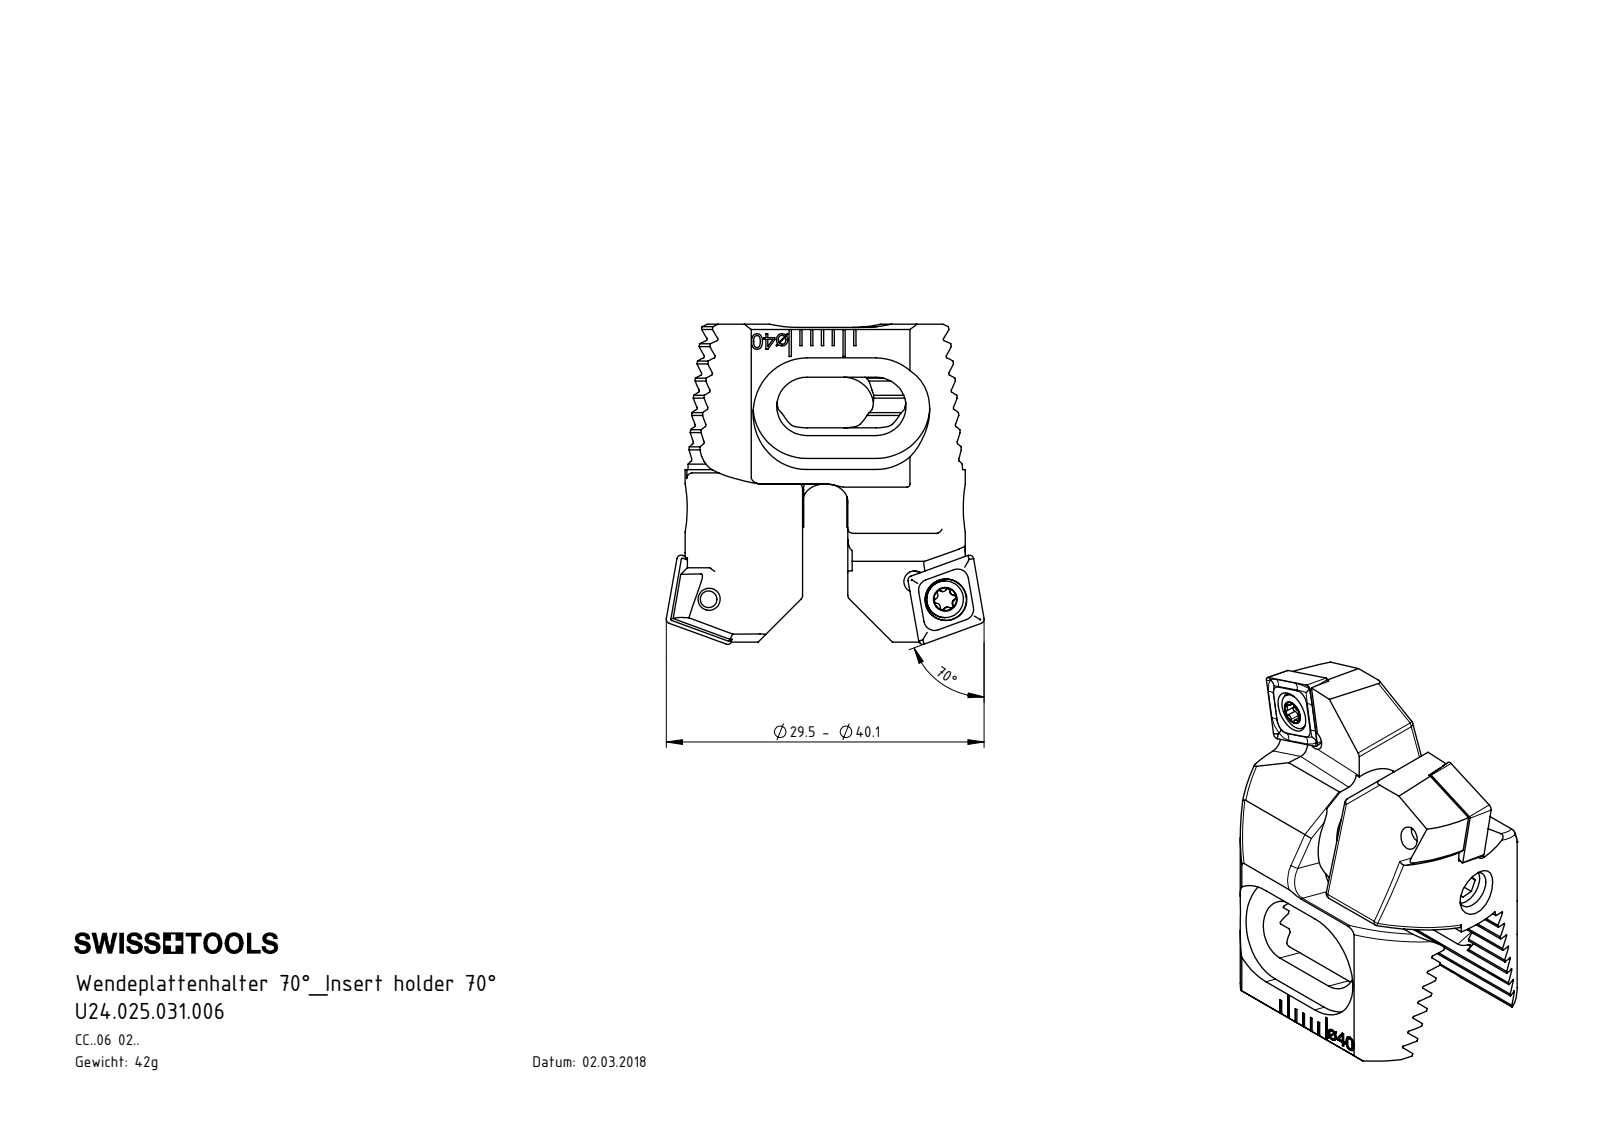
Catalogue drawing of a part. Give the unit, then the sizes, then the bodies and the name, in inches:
Units: inches
Overall size (bounding box): 1.169 × 1.161 × 0.799
Round holes (diameter × count): ⌀0.063 ×2, ⌀0.079 ×2, ⌀0.081 ×2, ⌀0.11 ×2, ⌀0.152 ×2, ⌀0.138 ×1
Round bosses / shafts (diameter × count): ⌀0.134 ×2, ⌀0.098 ×2, ⌀0.157 ×1
Partial cylindrical surfaces — rounded edges, fillets, slot ends (radius × count): R0.005 ×16, R0.02 ×16, R0.008 ×12, R0.014 ×10, R0.039 ×4, R0.079 ×4, R0.11 ×4, R0.197 ×4
Main face-to-face distances: 0.056, 0.113, 0.169, 0.225, 0.281, 0.154, 0.181, 0.338, 0.394, 0.016
Hole centre spacings: 0.129, 0.132, 0.276, 0.767, 0.77, 0.878, 0.532, 0.652
Volume: 0.318 in³ · Surface area: 7.401 in²
Bodies: 8 solids, 568 faces (316 planar, 112 cylindrical, 140 other)
Part name (STEP PRODUCT): Z25-ER3.001.010_A; Z25.WCA.B70.016; CCMT060204; WCA-ER2.001.006_A (+1 more)
STEP written by: SolidWorks 2017 (AUTOMOTIVE_DESIGN)
